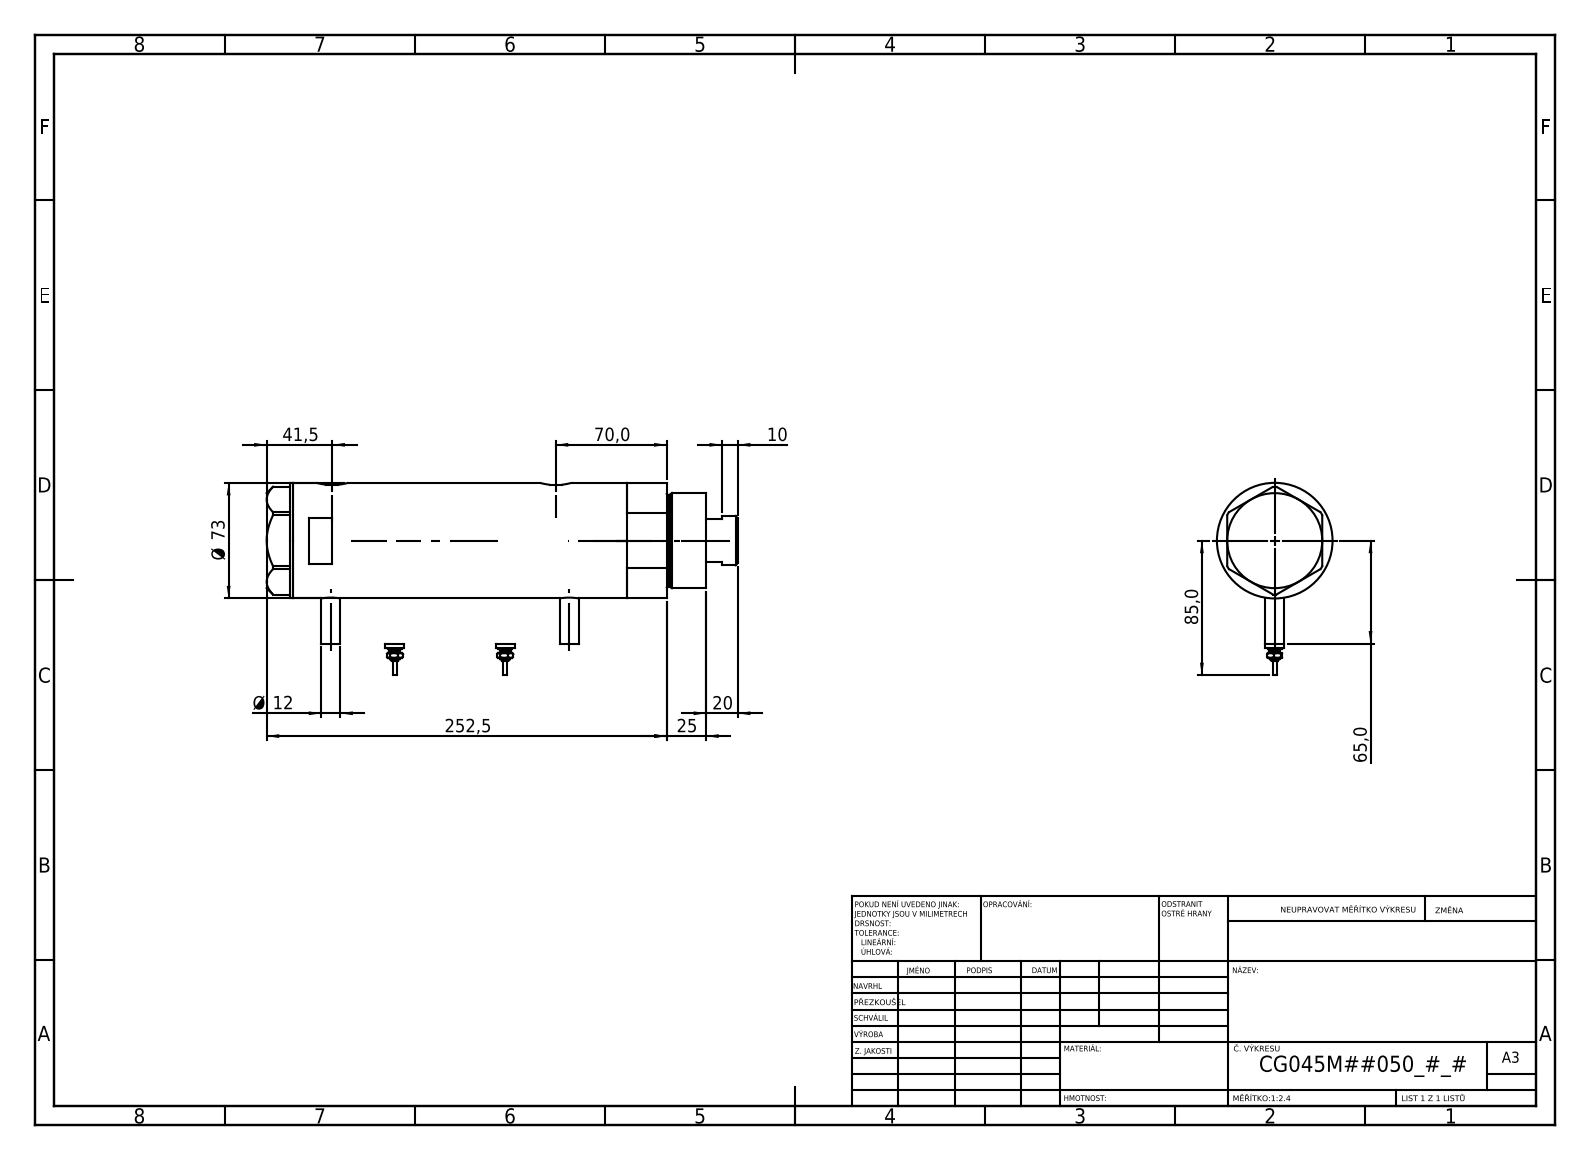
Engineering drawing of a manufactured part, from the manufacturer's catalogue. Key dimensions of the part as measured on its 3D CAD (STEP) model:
Part name (STEP PRODUCT): V270CG_FRONT; V270CG_BACK; V270CG_MIDDLE; V270CG_VC (+1 more)
STEP written by: SolidWorks 2019 (CONFIG_CONTROL_DESIGN)
Units: millimetres
Bodies: 6 solids, 212 faces (77 planar, 71 cylindrical, 64 other)
Overall size (bounding box): 297.5 × 121.5 × 73
Volume: 1 081 000 mm³ · Surface area: 174 773 mm²
Round holes (diameter × count): ⌀12.5 ×2, ⌀13.16 ×2, ⌀10.5 ×1, ⌀32 ×1, ⌀33.5 ×1, ⌀45 ×1, ⌀48 ×1, ⌀64 ×1
Round bosses / shafts (diameter × count): ⌀12 ×4, ⌀9 ×2, ⌀7 ×2, ⌀4.5 ×2, ⌀2.5 ×2, ⌀73 ×1, ⌀60 ×1, ⌀58 ×1
Partial cylindrical surfaces — rounded edges, fillets, slot ends (radius × count): R10 ×2
Main face-to-face distances: 166, 26, 140, 16.5, 42.5, 182.5, 2, 261, 277.5, 235
Hole centre spacings: 1, 8.5, 141, 142, 149.5, 150.5
